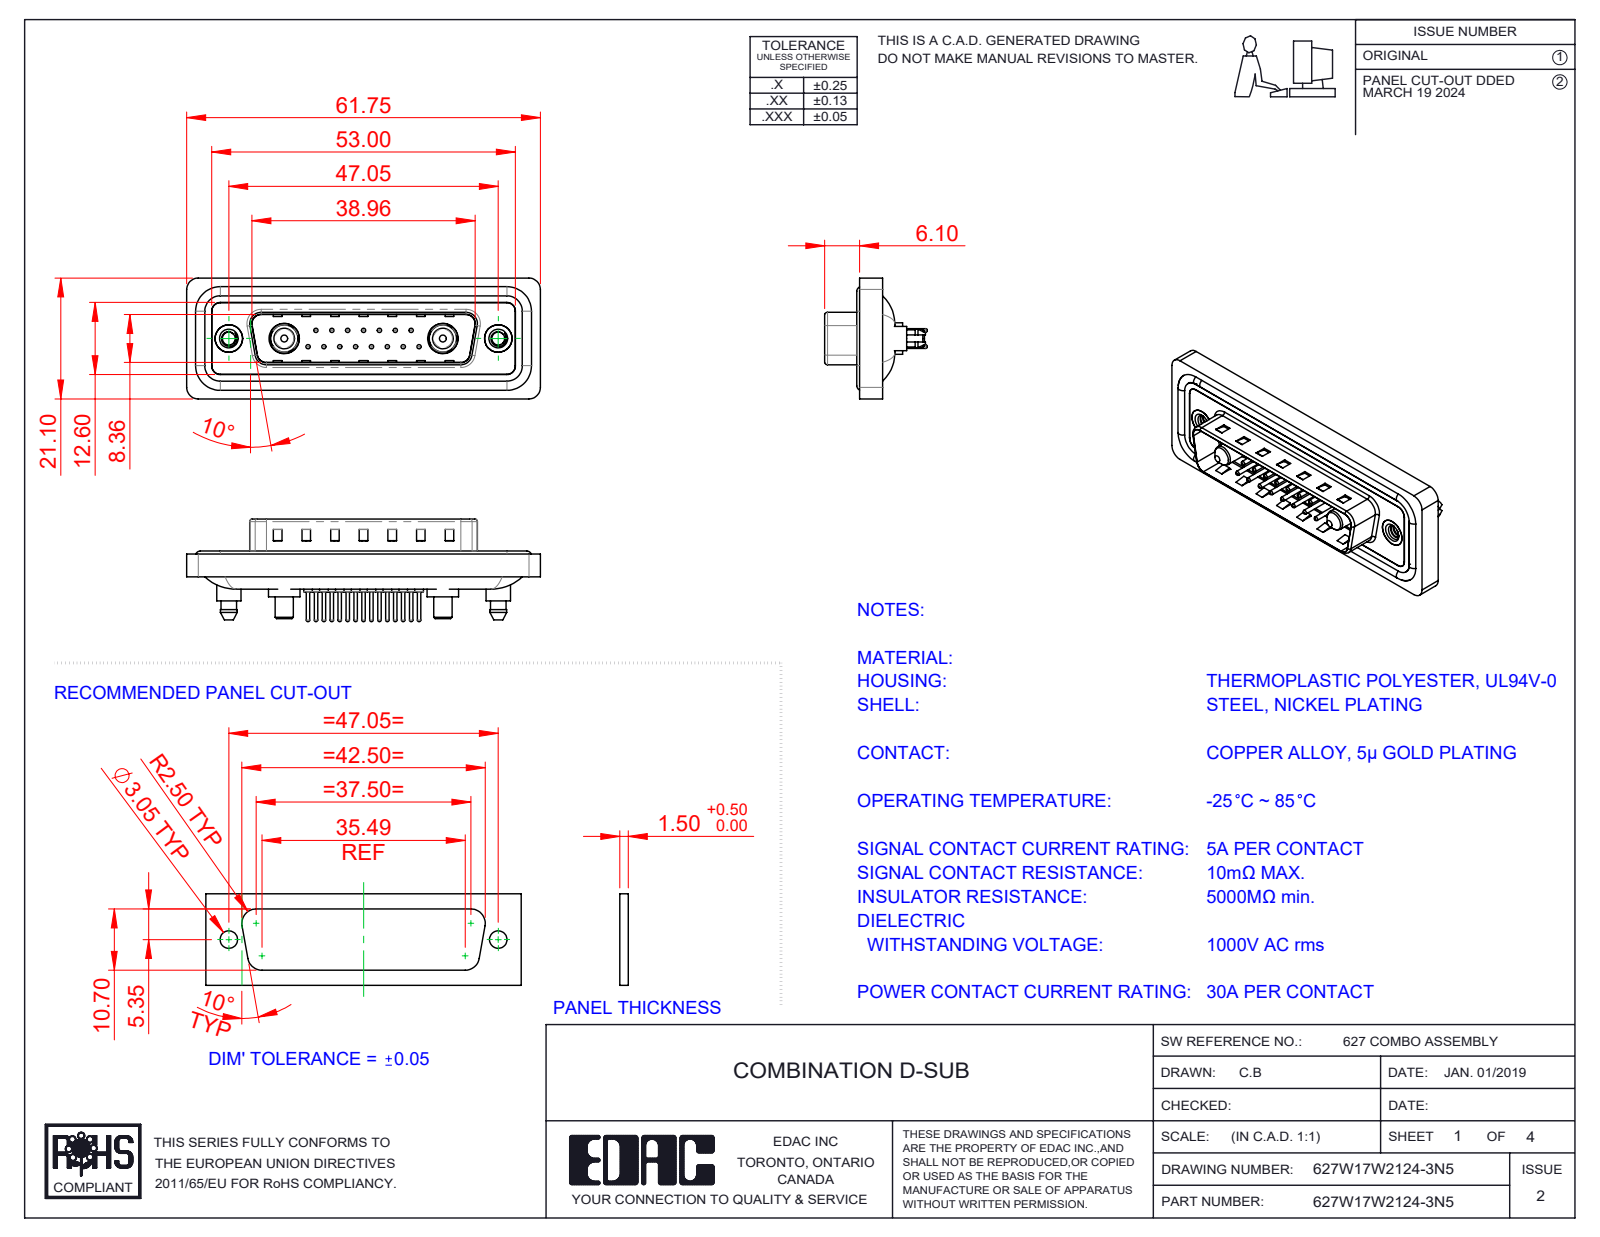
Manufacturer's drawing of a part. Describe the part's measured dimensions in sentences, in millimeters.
The part is named "627W17W2124-3N5; Power Pin_30A S; 627Combo Housing_17W2; 627Combo Waterproof Housing_25 Contacts (+5 more)". Its 3-D file was written by "SolidWorks 2023 (CONFIG_CONTROL_DESIGN)". It is 26 solids with 1166 faces: 350 planar, 468 cylindrical and 348 other. Overall it measures 61.75 by 21.1 by 17.9 millimeters. Its volume is 7 414 cubic millimeters and its surface area 12 256 square millimeters. Round holes: 15 of diameter 0.75, 15 of diameter 1.6, 15 of diameter 2, 2 of diameter 2.26, 2 of diameter 4, 2 of diameter 4.8, 2 of diameter 4.85, 2 of diameter 5, 2 of diameter 5.3. Round bosses or shafts: 15 of diameter 1.5, 15 of diameter 0.6, 4 of diameter 1.6, 2 of diameter 5.5, 2 of diameter 5.4, 2 of diameter 5.2, 2 of diameter 4.9, 2 of diameter 4.75. Partial cylindrical surfaces (rounded edges, fillets, slot ends): 24 of radius 1.5, 18 of radius 2, 10 of radius 1.6, 8 of radius 0.5, 4 of radius 0.25, 4 of radius 0.6, 4 of radius 0.65, 4 of radius 0.9. The main face-to-face distances are 0.4, 1.5, 1.1, 1.6, 0.5, 3.1, 2.9, 0.82, 9.58, 4.1. The hole center spacings are 3.16, 2.77, 5.54, 8.31, 5.04, 7.49, 11.08, 5.03.
